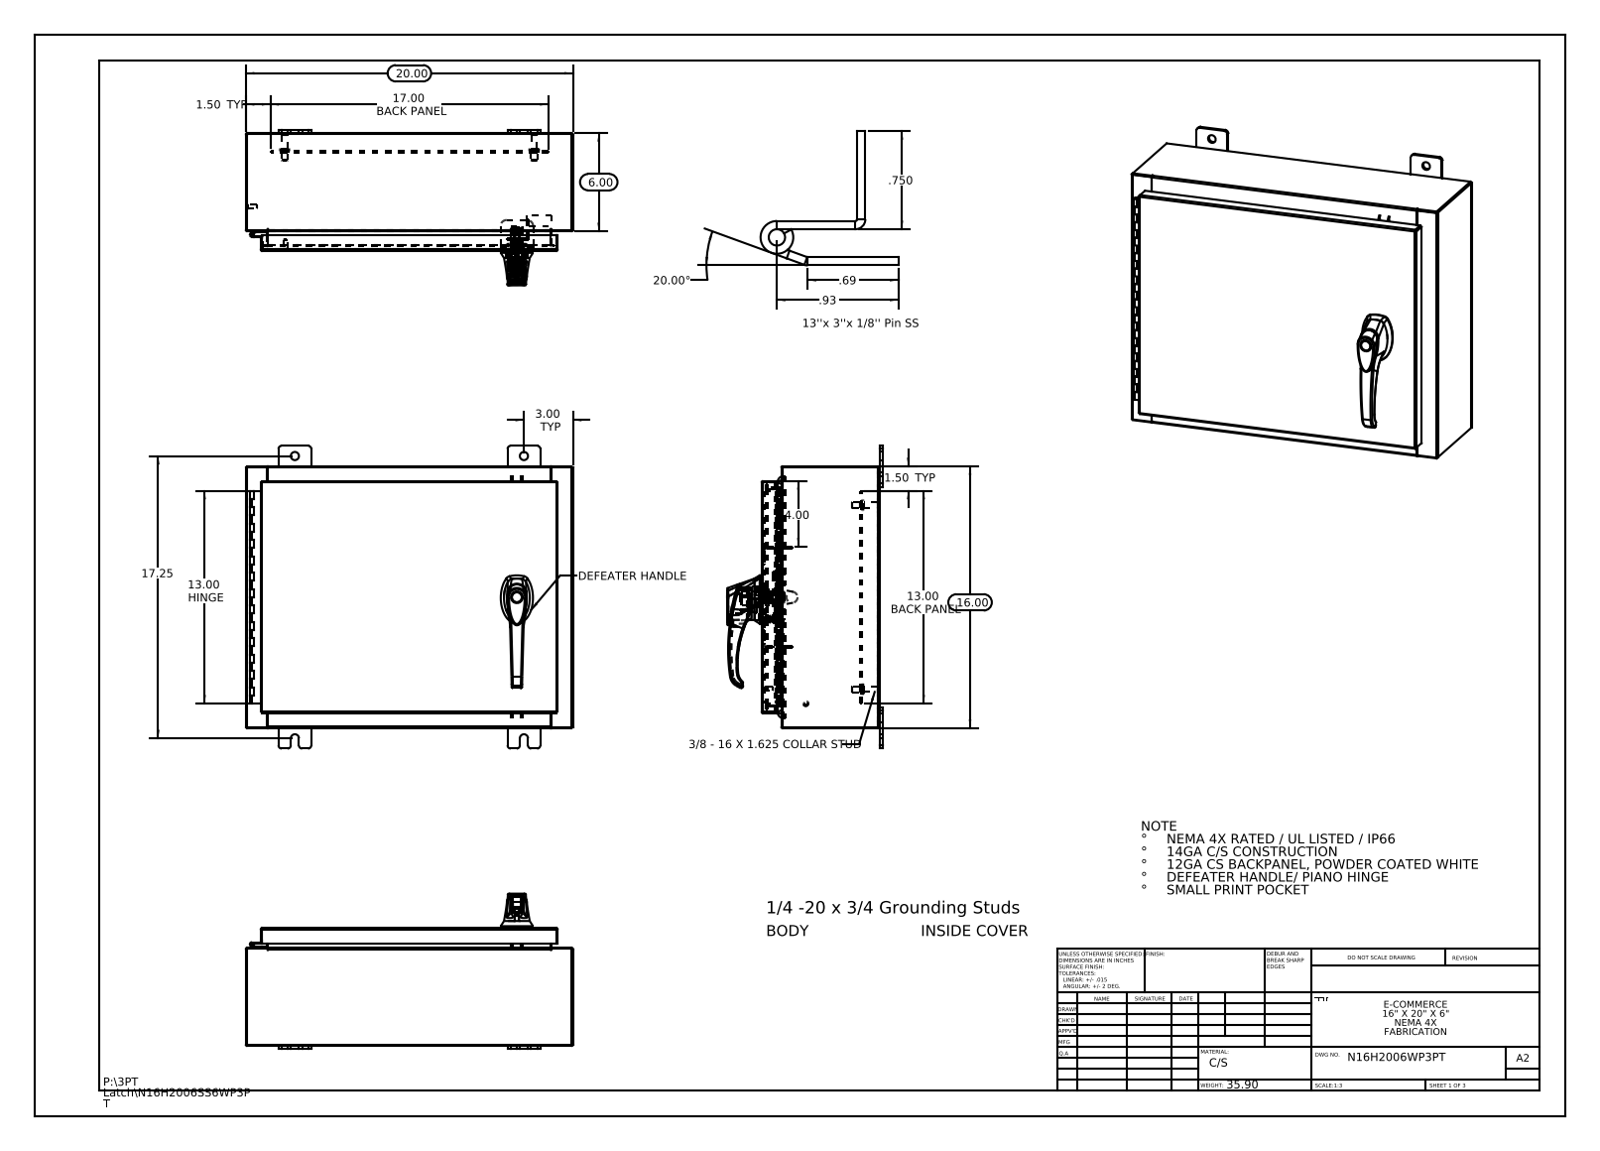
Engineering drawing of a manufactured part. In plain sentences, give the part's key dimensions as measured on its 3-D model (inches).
The part is named "N16H2006SS6WP3PT Top; 012103_012102; N16H2006SS6WP3PT Cover; N16H2006SS6WP3PT 125 Pin Hinge (+8 more)". Its 3-D file was written by "SolidWorks 2013 (CONFIG_CONTROL_DESIGN)". It is 31 solids with 2204 faces: 757 planar, 793 cylindrical and 654 other. Overall it measures 20 by 18.5 by 9.495 inches. Its volume is 128.5 cubic inches and its surface area 3 155 square inches. Round holes: 8 of diameter 0.5, 4 of diameter 0.25, 3 of diameter 0.138, 3 of diameter 0.161, 2 of diameter 0.079, 2 of diameter 0.203, 2 of diameter 0.313, 2 of diameter 0.437, 1 of diameter 0.125, 1 of diameter 0.125, 1 of diameter 0.197, 1 of diameter 0.276. Round bosses or shafts: 4 of diameter 0.625, 4 of diameter 0.375, 4 of diameter 0.33, 1 of diameter 1.181, 1 of diameter 0.748, 1 of diameter 0.68, 1 of diameter 0.661, 1 of diameter 0.639. Partial cylindrical surfaces (rounded edges, fillets, slot ends): 37 of radius 0.118, 33 of radius 0.006, 24 of radius 0.19, 20 of radius 0.013, 18 of radius 0.088, 15 of radius 0.039, 12 of radius 0.028, 6 of radius 0.008. The main face-to-face distances are 0.075, 7.126, 7.051, 7.201, 15.925, 1, 0.104, 1.075, 6.051, 6.126. The hole center spacings are 3.708, 0.295, 0.625, 0.841, 1.25, 1.313, 1.32, 1.484.
